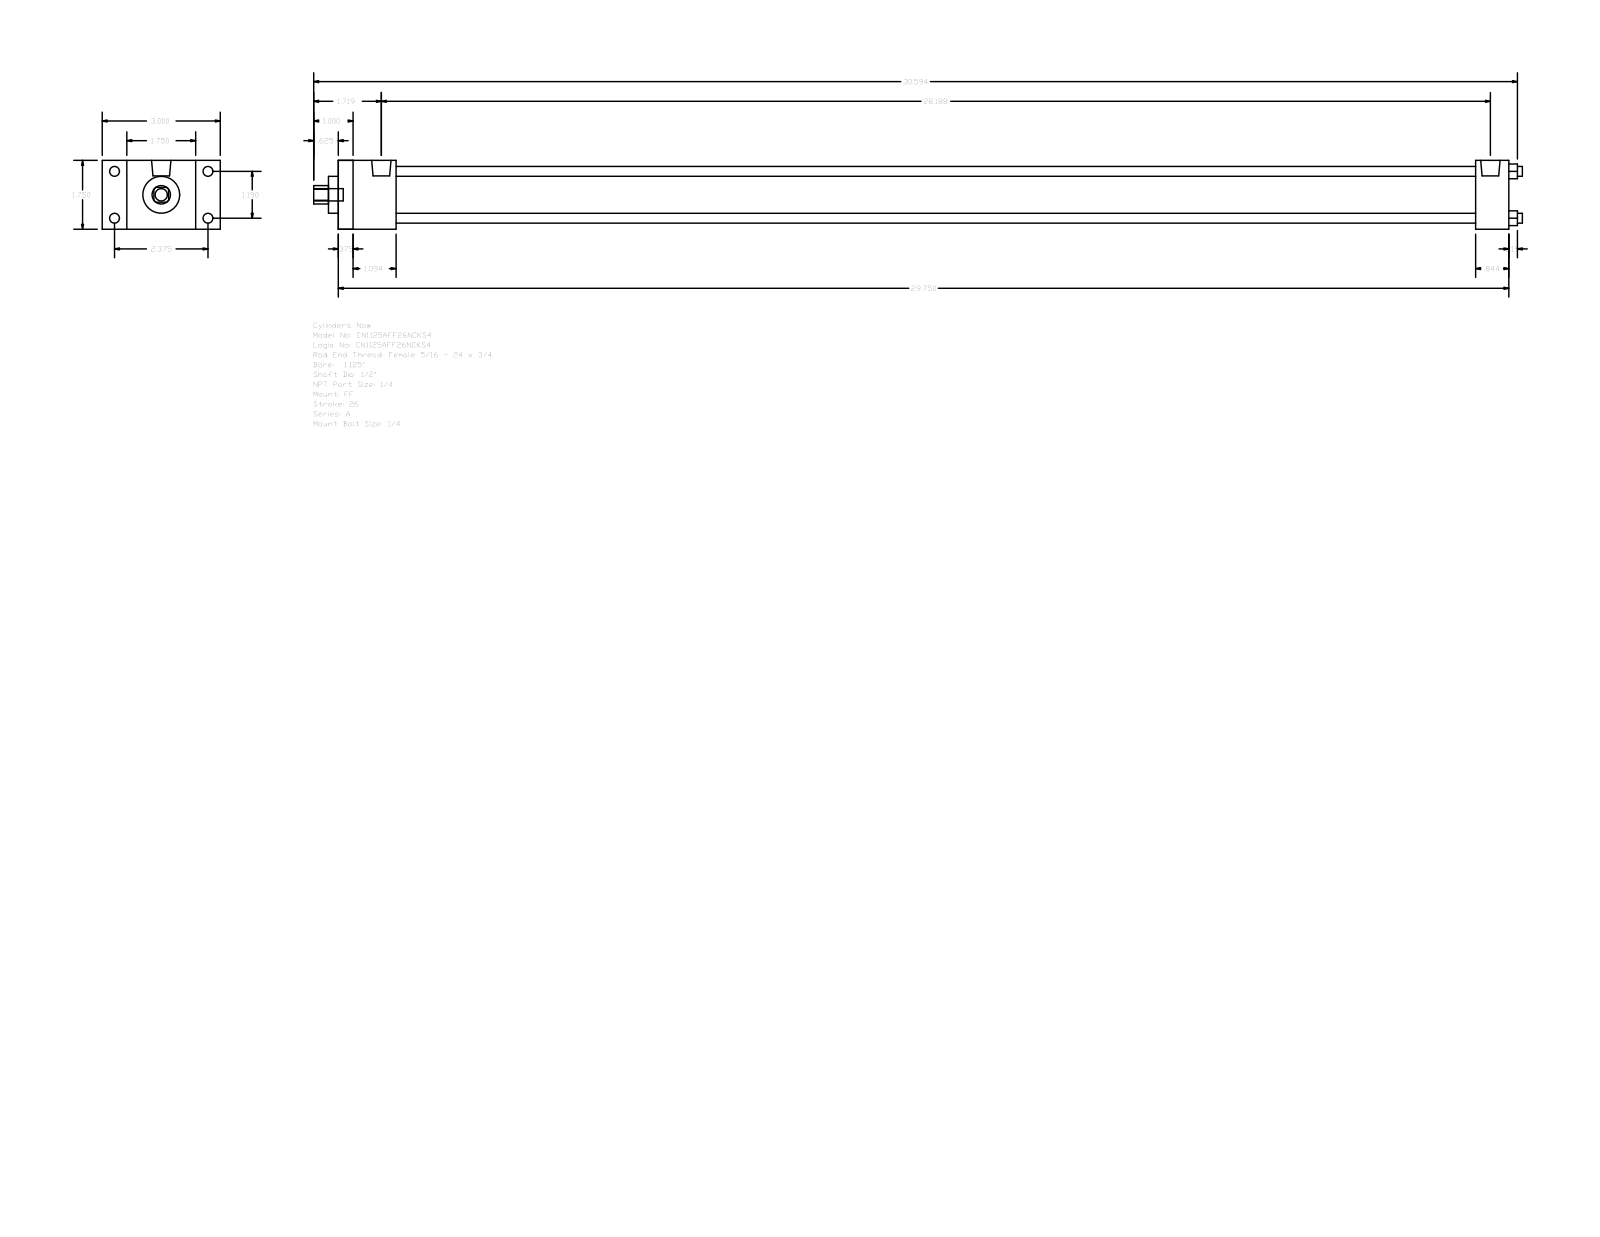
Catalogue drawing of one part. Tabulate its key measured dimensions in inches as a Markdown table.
| quantity | value |
| --- | --- |
| part name | A_FF__0112_0.5 |
| STEP written by | GSSL Pune (CONFIG_CONTROL_DESIGN) |
| units | inches |
| bodies | 0 solids, 92 faces (64 planar, 28 cylindrical, 0 other) |
| overall size | 30.719 × 3 × 1.75 |
| round holes (diameter × count) | 0.25 × 4, 0.5 × 1, 0.937 × 1, 1.255 × 1 |
| round bosses / shafts (diameter × count) | 0.25 × 4, 0.219 × 4, 0.492 × 2, 0.313 × 1 |
| partial cylindrical surfaces (radius × count) | 0.234 × 1 |
| main face-to-face distances | 1.75, 29.75, 0.375, 29.375, 0.625, 28.906, 28.531, 0.844, 1.469, 1.094 |
| hole center spacings | 0.841, 1.19, 1.683 |
